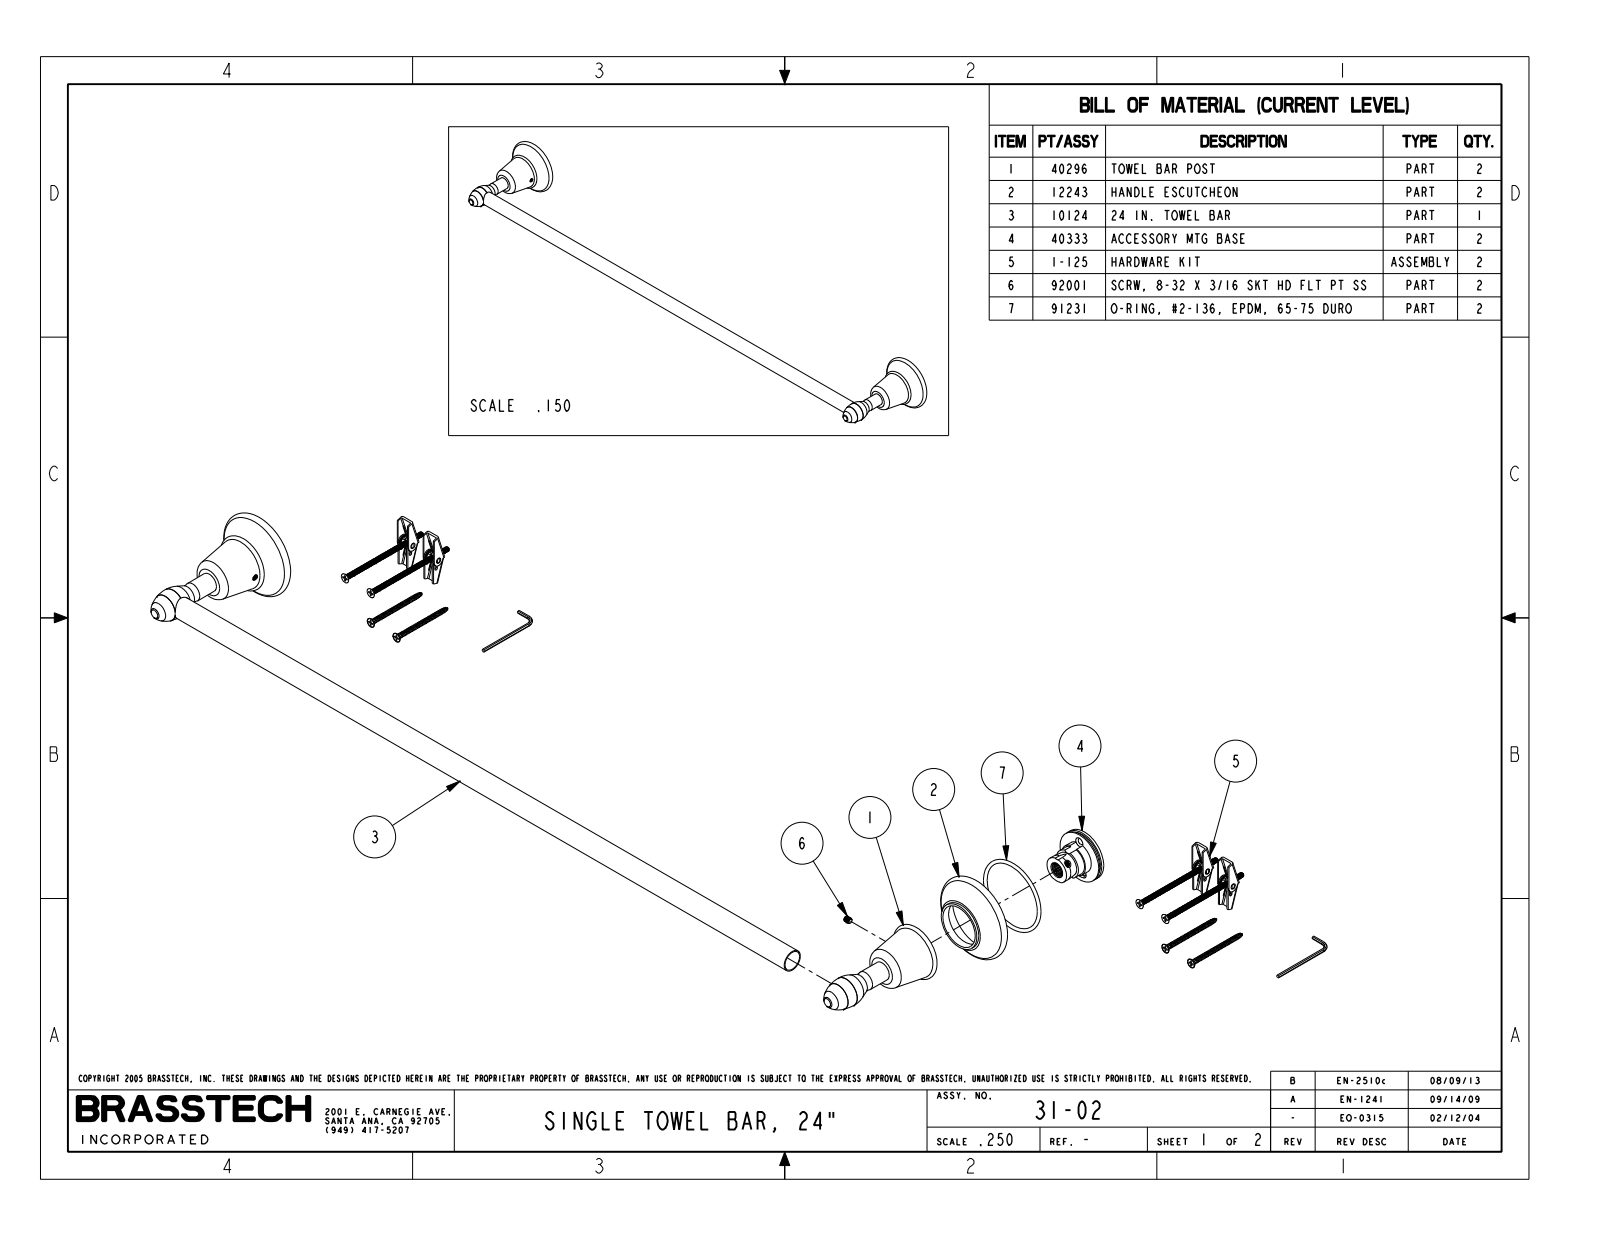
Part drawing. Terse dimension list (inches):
name: 31-02_WEB
written by: PRO/ENGINEER BY PARAMETRIC TECHNOLOGY CORPORATION, 2009300 (CONFIG_CONTROL_DESIGN)
unit: in
bodies: 0 solids, 118 faces (6 planar, 50 cylindrical, 62 other)
size: 26.6 × 4.153 × 2.35
holes: 1× ⌀0.136
bosses: 2× ⌀0.553, 1× ⌀0.625
face distances: 1.975, 23.115
